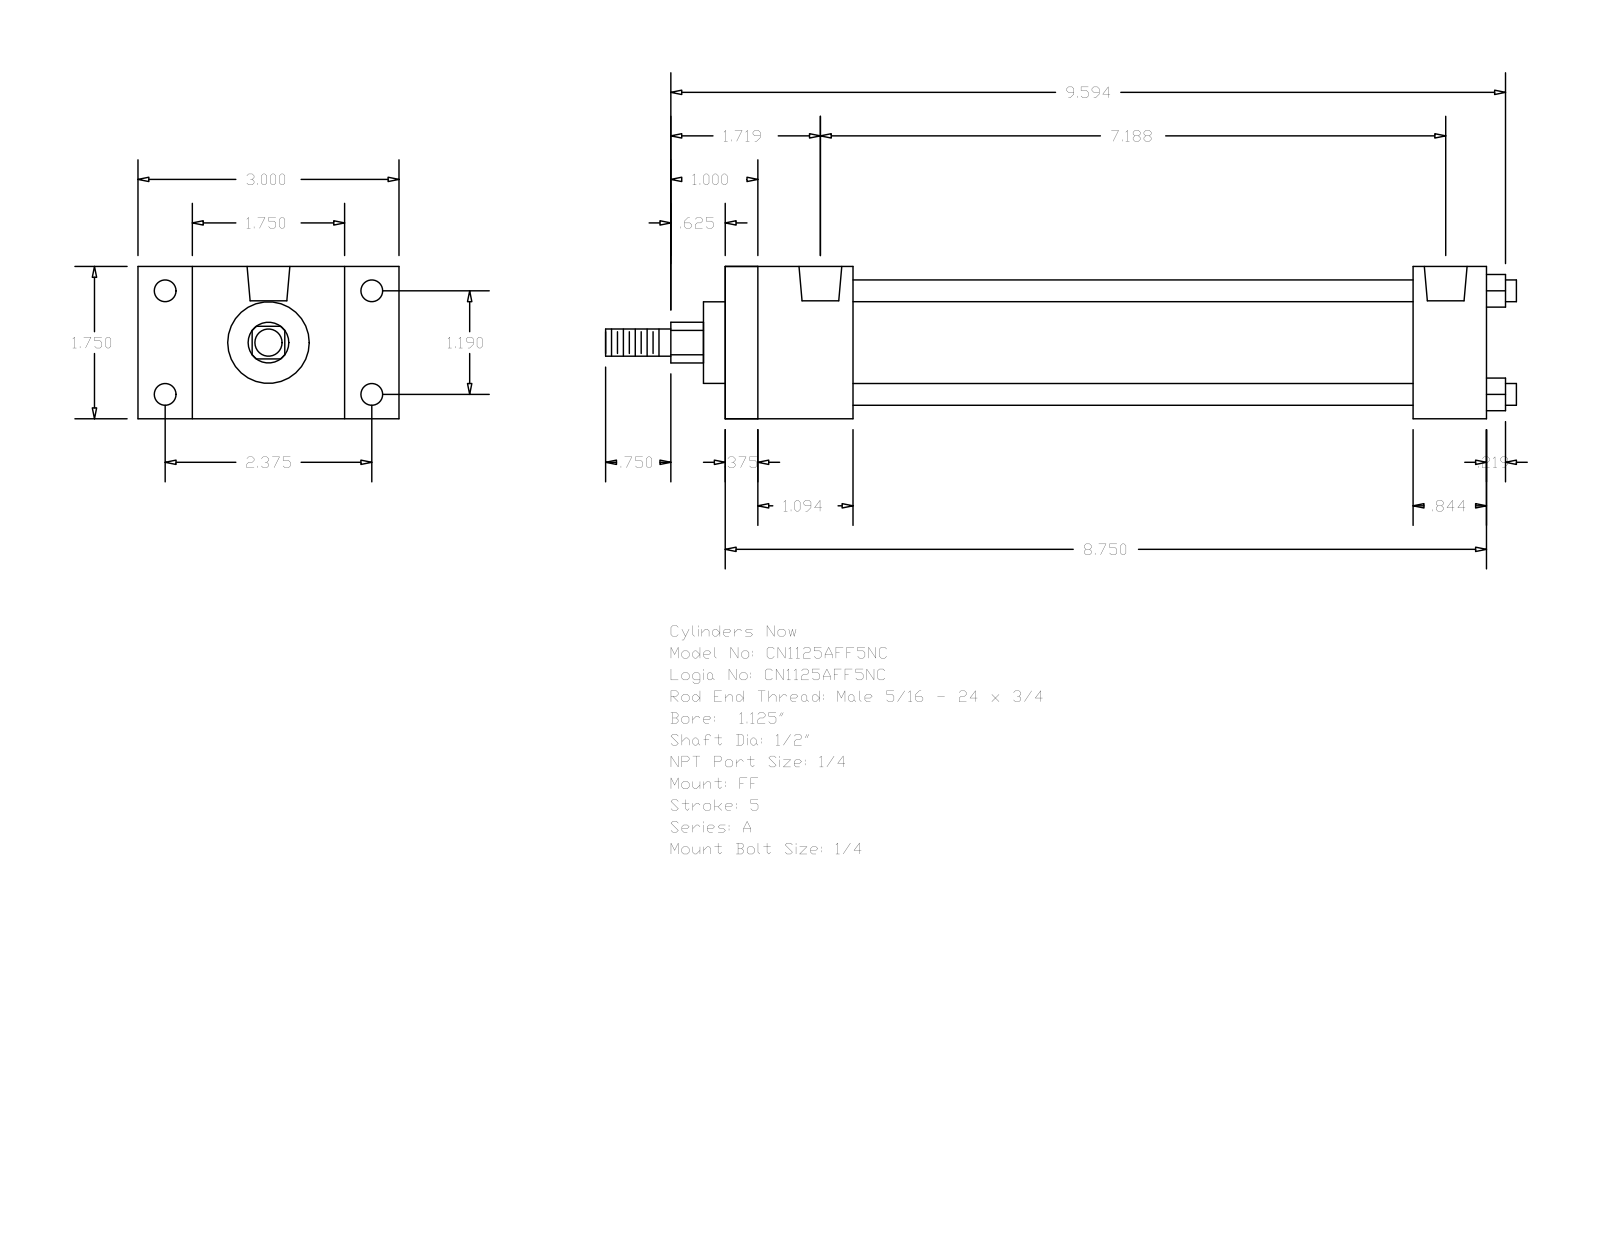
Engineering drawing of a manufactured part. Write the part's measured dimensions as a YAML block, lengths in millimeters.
part_name: "A_FF__0112_0.5"
step_written_by: "GSSL Pune (CONFIG_CONTROL_DESIGN)"
units: millimeters
bodies: {solids: 0, faces: 92, planar: 64, cylindrical: 28, other: 0}
overall_size: [265.91, 76.2, 44.45]
round_holes:
  - {diameter: 5.56, count: 4}
  - {diameter: 6.35, count: 4}
  - {diameter: 12.49, count: 2}
round_bosses_or_shafts:
  - {diameter: 6.35, count: 4}
  - {diameter: 31.88, count: 1}
  - {diameter: 23.81, count: 1}
  - {diameter: 12.7, count: 1}
  - {diameter: 7.94, count: 1}
partial_cylinders:
  - {radius: 5.94, count: 1}
face_to_face_distances: [44.46, 222.24, 9.52, 212.72, 15.87, 200.81, 191.29, 21.43, 37.3, 27.78]
hole_center_spacings: [30.22, 60.32, 67.47, 179.39, 1.58, 1.59, 180.97, 180.98]
